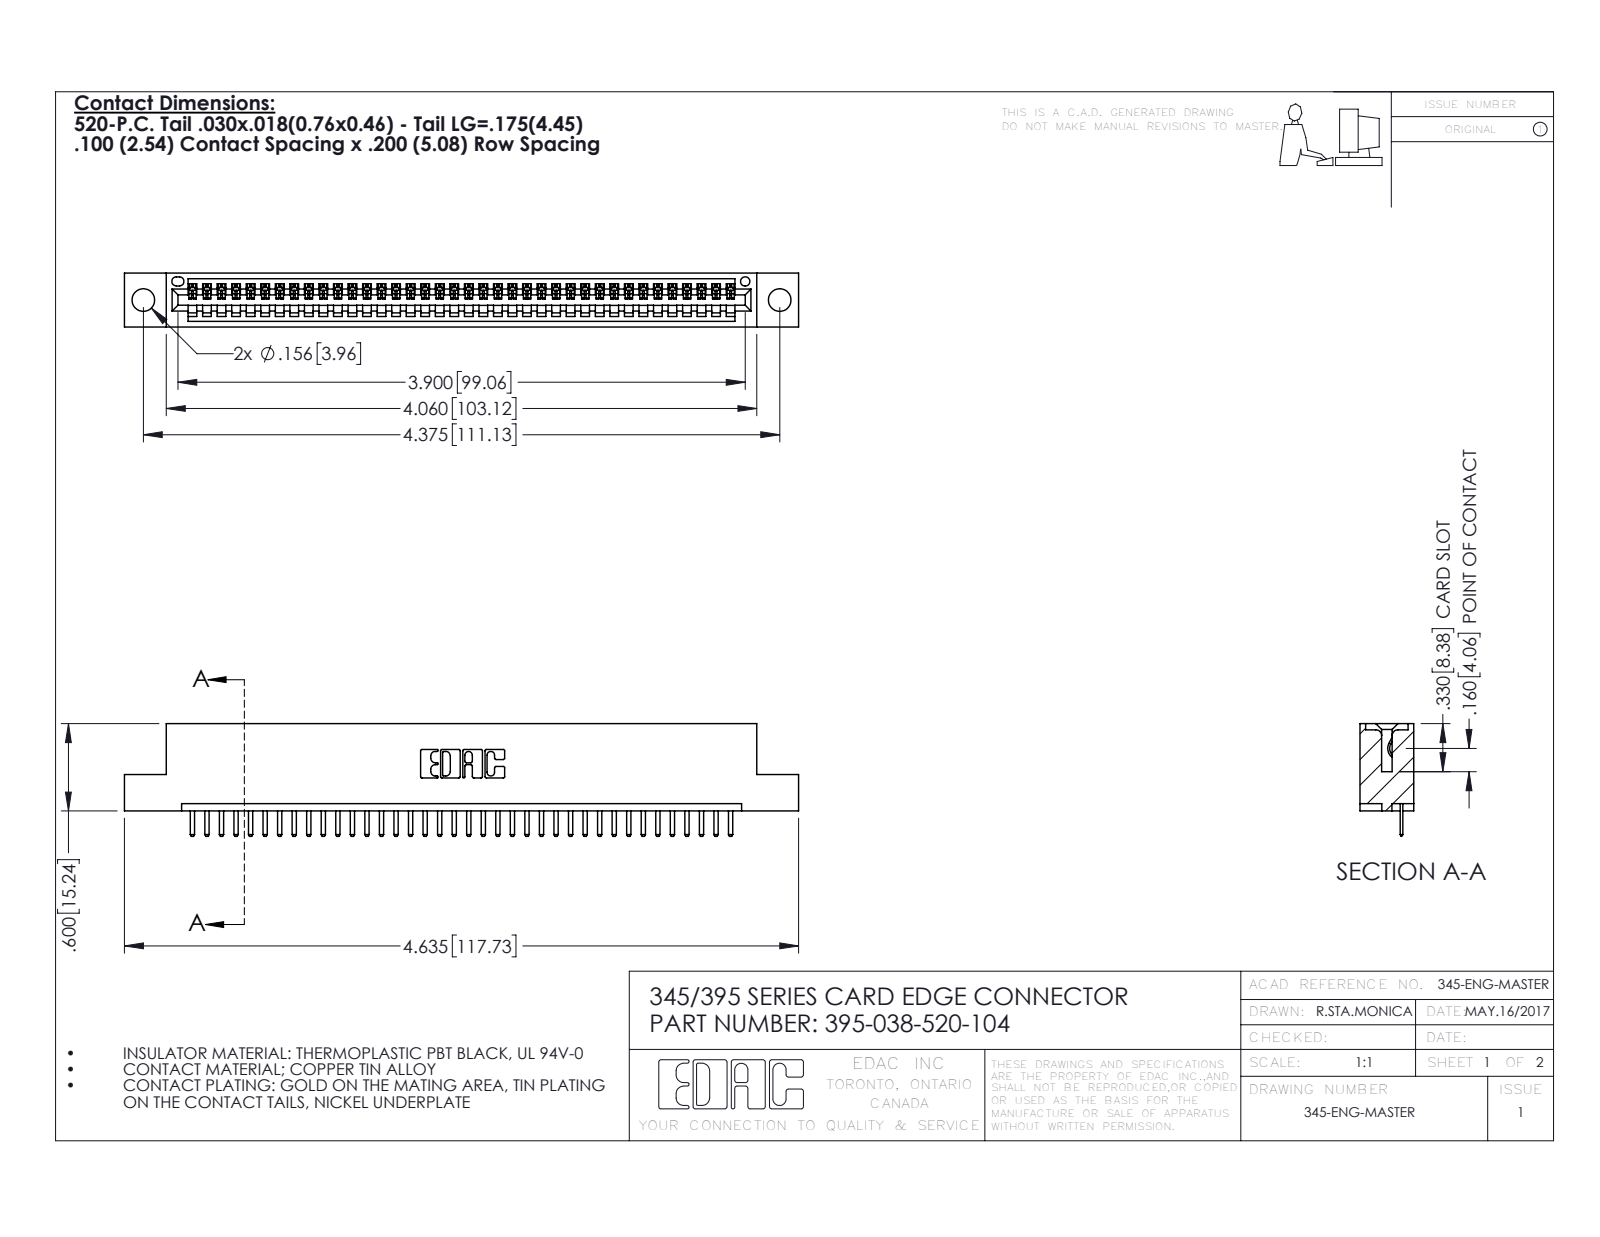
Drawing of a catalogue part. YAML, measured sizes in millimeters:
part_name: "345-292-001_345-293-120; 395-038-520-104; 345 Part_Flush Mounting Lugs - 0.156 Dia-TH"
step_written_by: "SolidWorks 2016 (CONFIG_CONTROL_DESIGN)"
units: millimeters
bodies: {solids: 39, faces: 2482, planar: 1676, cylindrical: 806, other: 0}
overall_size: [117.7, 19.7, 9.4]
volume: 10900
surface_area: 13950
round_holes:
  - {diameter: 4, count: 2}
  - {diameter: 1.6, count: 1}
partial_cylinders:
  - {radius: 0.3, count: 78}
  - {radius: 0.2, count: 76}
  - {radius: 0.3, count: 22}
  - {radius: 0.2, count: 6}
  - {radius: 0.8, count: 6}
  - {radius: 0.7, count: 3}
  - {radius: 0.8, count: 2}
  - {radius: 1, count: 2}
face_to_face_distances: [7.6, 1.8, 9.4, 5.1, 2.5, 6.9, 0.6, 5.7, 1.8, 3.8]
hole_center_spacings: [6.9, 105.1, 111.1]
